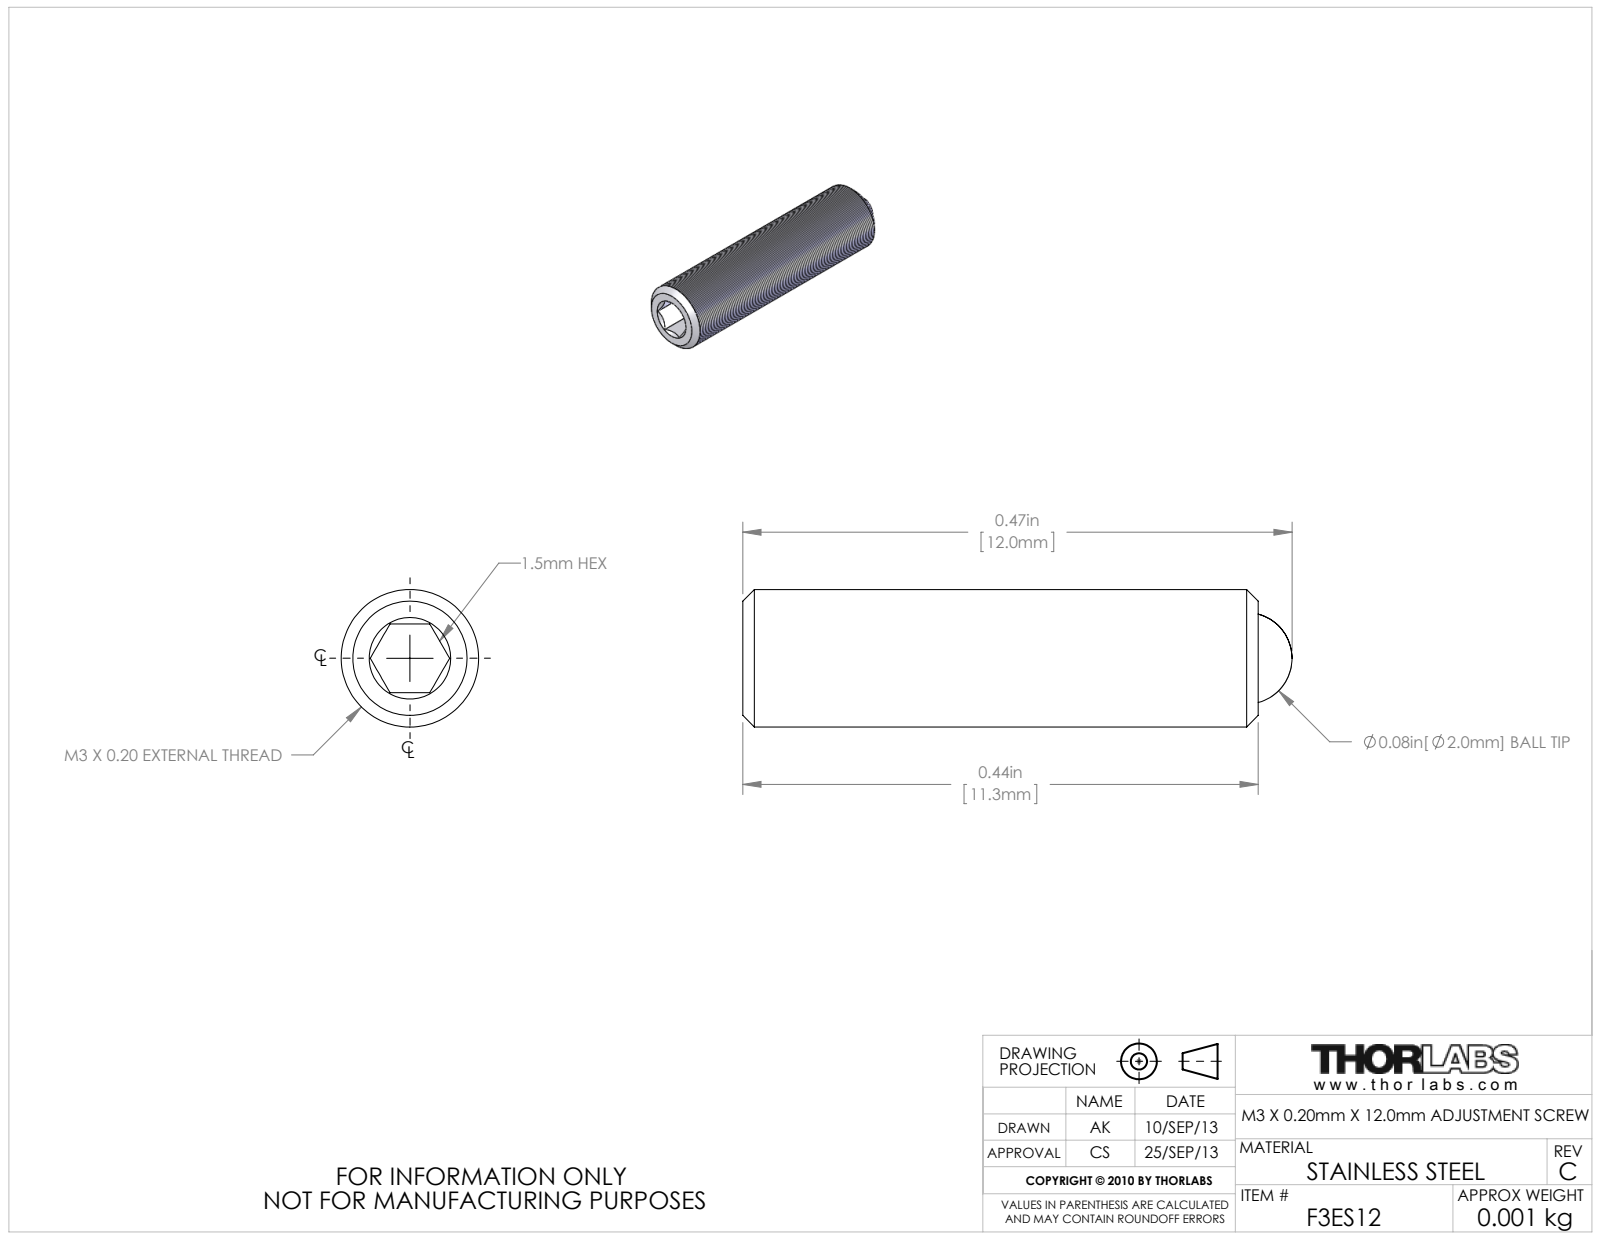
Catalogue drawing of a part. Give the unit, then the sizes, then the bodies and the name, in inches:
Units: inches
Overall size (bounding box): 0.472 × 0.118 × 0.118
Round holes (diameter × count): ⌀0.079 ×1
Round bosses / shafts (diameter × count): ⌀0.118 ×1
Main face-to-face distances: 0.059, 0.12, 0.323, 0.443
Volume: 0.005 in³ · Surface area: 0.234 in²
Bodies: 2 solids, 25 faces (9 planar, 4 cylindrical, 12 other)
Part name (STEP PRODUCT): 8565-E0W
STEP written by: SolidWorks 2012 (AUTOMOTIVE_DESIGN)
